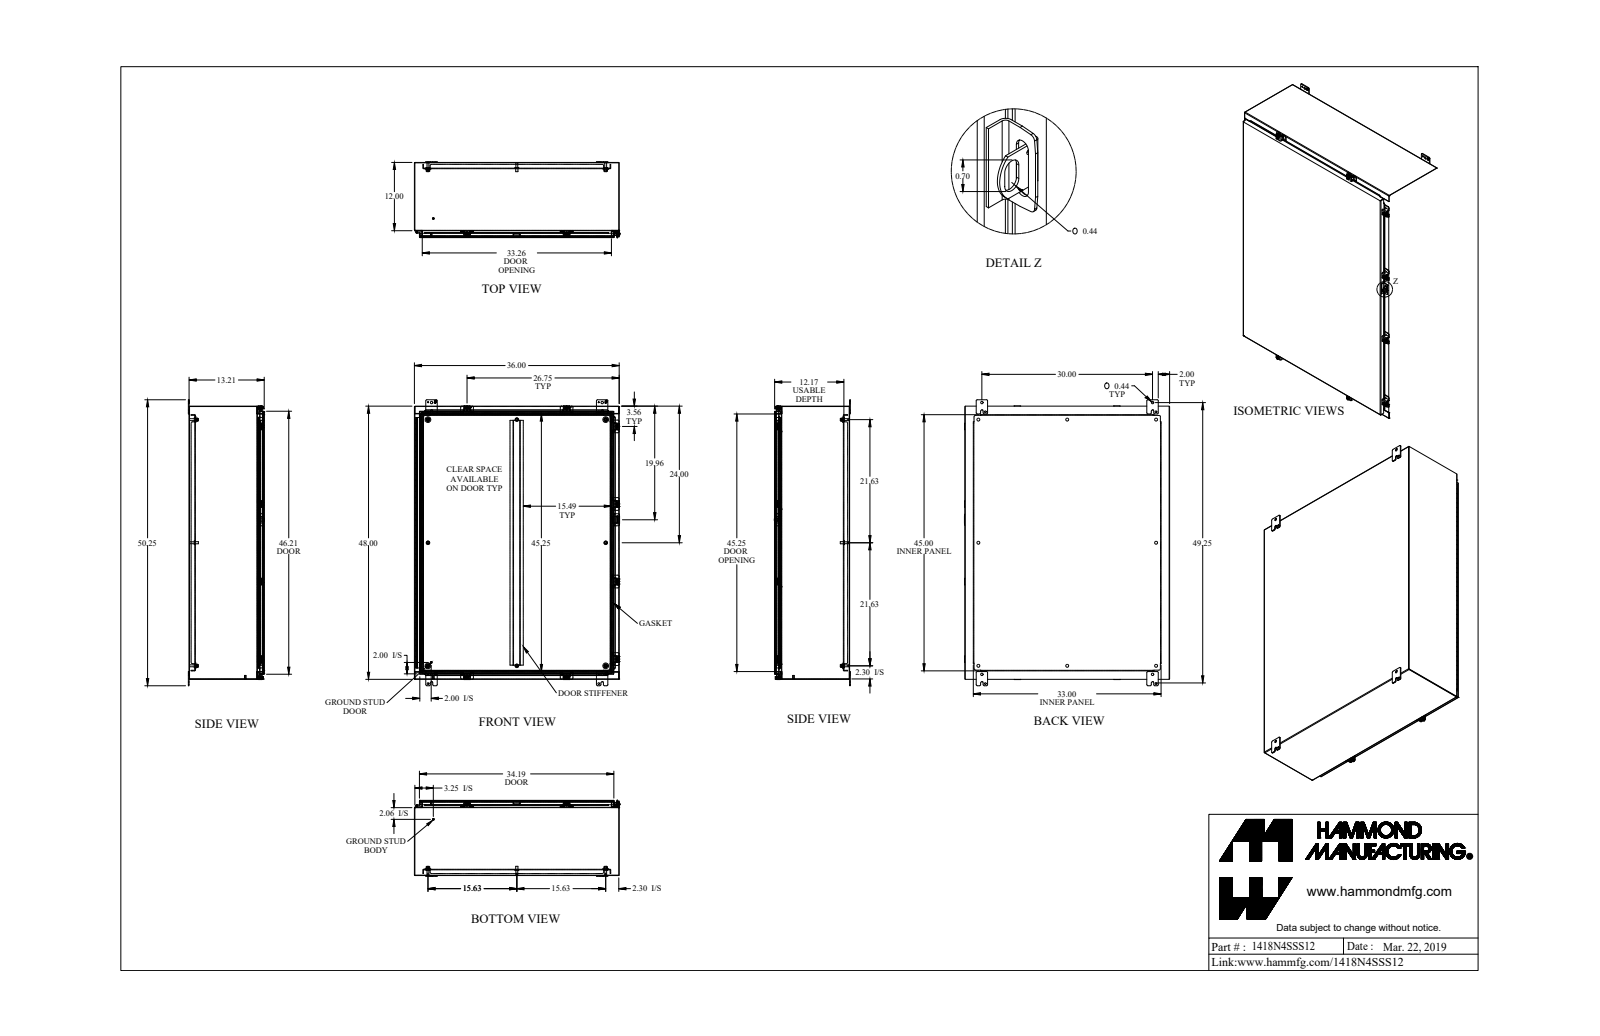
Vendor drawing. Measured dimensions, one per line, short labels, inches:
name: 1418N4SSS12_Default
written by: SolidWorks 2019 (CONFIG_CONTROL_DESIGN)
unit: in
bodies: 66 solids, 2324 faces (1411 planar, 829 cylindrical, 84 other)
size: 50.25 × 36.063 × 13.375
volume: 609.6 in³; area: 15 930 in²
holes: 8× ⌀0.213, 8× ⌀0.265, 8× ⌀0.375, 8× ⌀0.5, 4× ⌀0.307, 4× ⌀0.313, 4× ⌀0.437, 4× ⌀0.445, 1× ⌀0.125, 1× ⌀0.187
bosses: 8× ⌀0.65, 8× ⌀0.5, 8× ⌀0.39, 8× ⌀0.375, 8× ⌀0.332, 8× ⌀0.244, 4× ⌀1, 2× ⌀0.313
rounds: 44× R0.25, 39× R0.048, 39× R0.143, 30× R0.188, 22× R0.036, 22× R0.108, 16× R0.141, 12× R0.125
face distances: 0.072, 13.066, 13.138, 0.072, 0.095, 13.138, 13.21, 0.937, 1.009, 12.106
hole spacings: 38.003, 31.25, 51.507, 21.625, 45.893, 45.986, 53.358, 7.196
